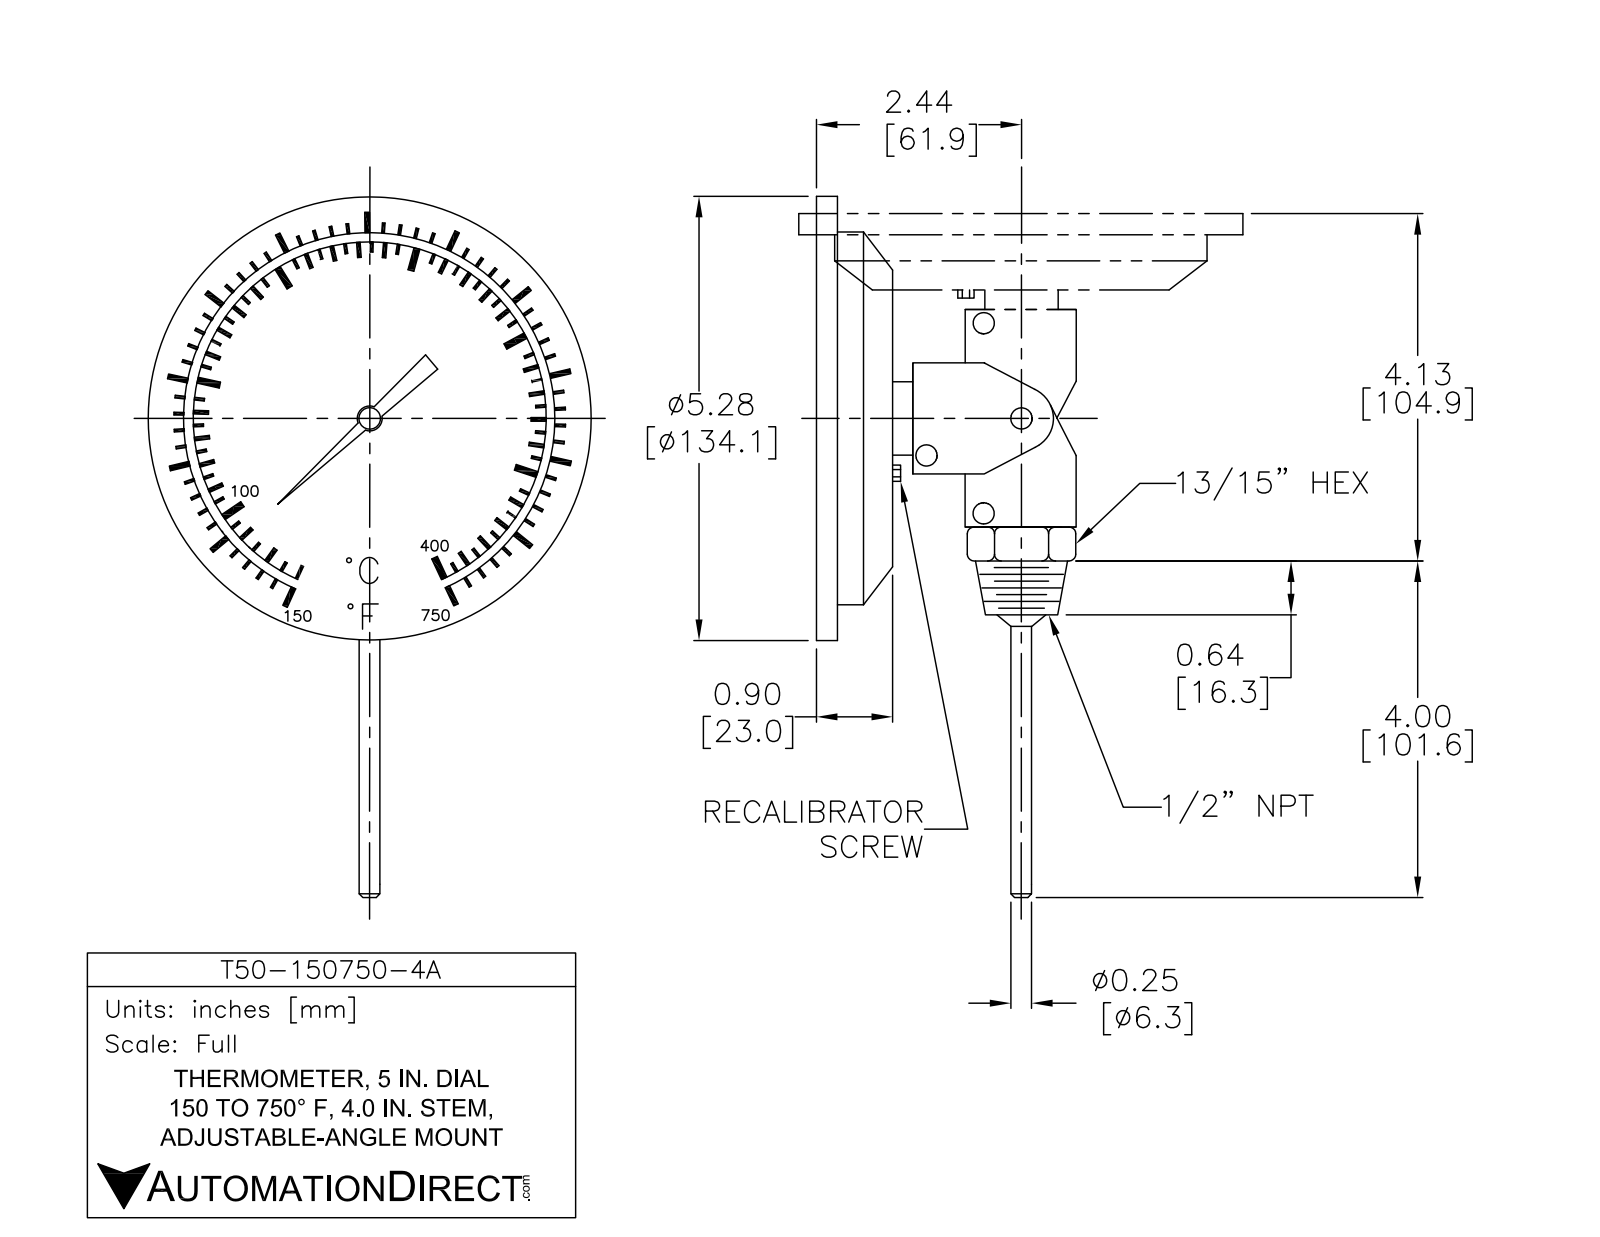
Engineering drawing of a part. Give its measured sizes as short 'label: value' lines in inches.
name: T50-150750-4A
written by: SolidWorks 2021 (AUTOMOTIVE_DESIGN)
unit: in
bodies: 1 solid, 500 faces (306 planar, 45 cylindrical, 149 other)
size: 7.96 × 5.28 × 5.28
volume: 10.13 in³; area: 96.79 in²
holes: 1× ⌀3.424, 1× ⌀3.706, 1× ⌀4.76, 1× ⌀4.836
bosses: 4× ⌀0.305, 2× ⌀0.145, 1× ⌀5.28, 1× ⌀4.97, 1× ⌀3.454, 1× ⌀0.85, 1× ⌀0.821, 1× ⌀0.544
rounds: 10× R0.06, 4× R0.04, 1× R0.17, 1× R0.336, 1× R0.336, 1× R0.342, 1× R0.4, 1× R1.868
face distances: 0.353, 0.074, 0.055, 0.427, 1.19, 0.815, 0.462, 0.388, 1.245, 2.435
